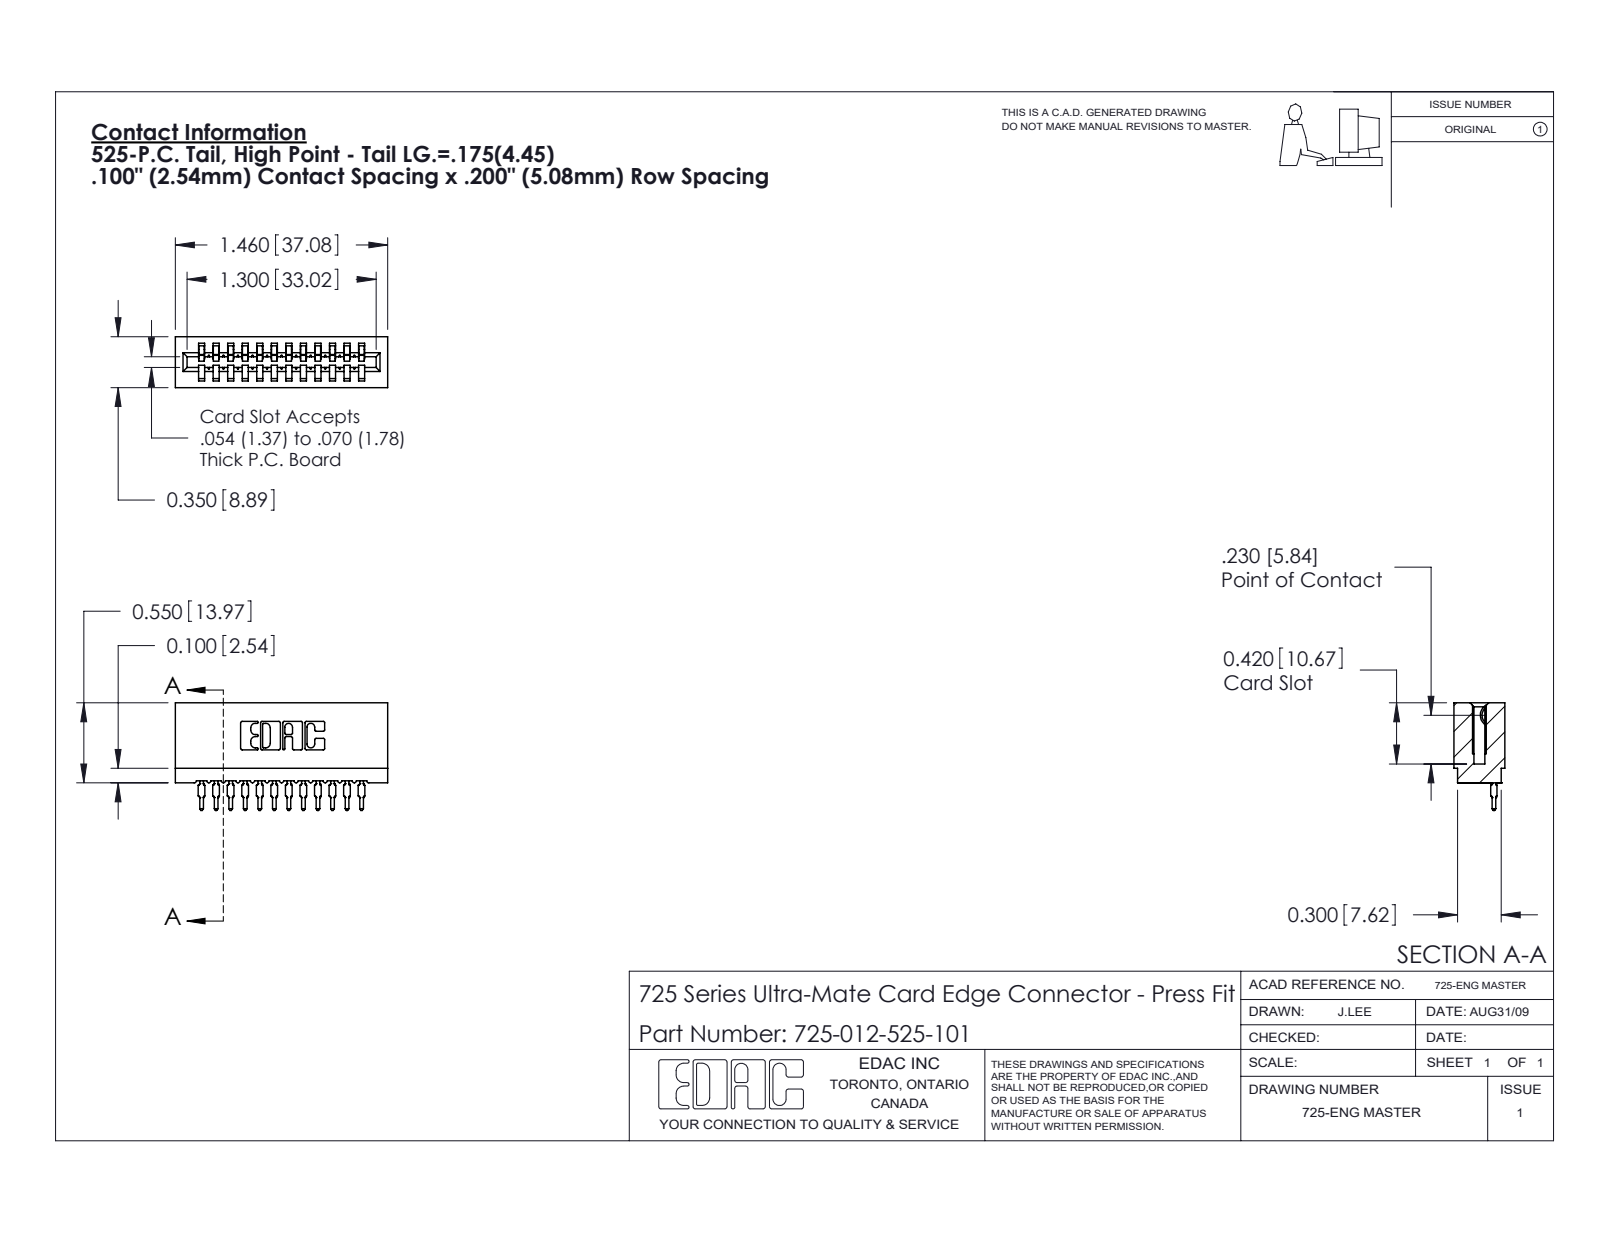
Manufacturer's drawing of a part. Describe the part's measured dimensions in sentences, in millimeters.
The part is named "725-012-525-101; 745-292-001_525; 725 Part_Insulator Option - 01". Its 3-D file was written by "SolidWorks 2020 (CONFIG_CONTROL_DESIGN)". It is 13 solids with 1439 faces: 859 planar, 268 cylindrical and 312 other. Overall it measures 37.1 by 18.8 by 8.9 millimeters. Its volume is 2 970 cubic millimeters and its surface area 5 152 square millimeters. Partial cylindrical surfaces (rounded edges, fillets, slot ends): 24 of radius 0.4, 24 of radius 0.5, 22 of radius 0.3, 6 of radius 0.2, 6 of radius 0.8, 4 of radius 0.1, 4 of radius 0.3, 3 of radius 0.7. The main face-to-face distances are 2.5, 5.1, 7.6, 10.2, 12.7, 15.2, 6.6, 4, 1.5, 1.1.
